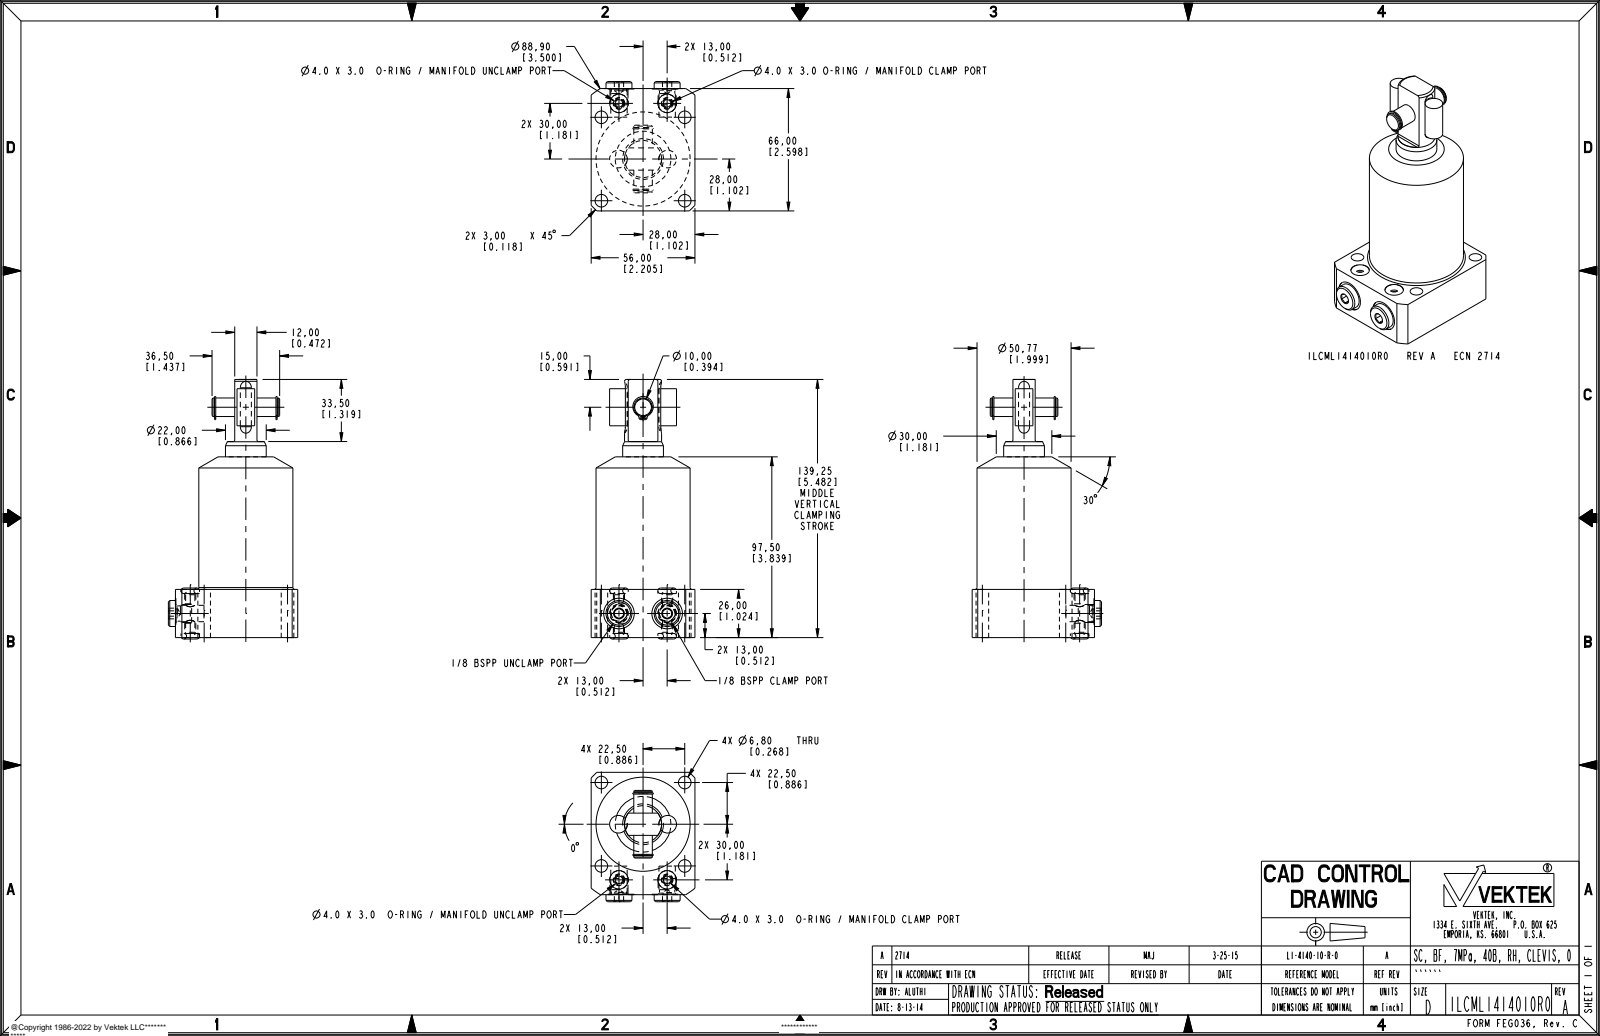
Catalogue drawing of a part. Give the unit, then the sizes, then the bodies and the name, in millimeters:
Units: millimetres
Overall size (bounding box): 140 × 69.81 × 56
Round holes (diameter × count): ⌀6.8 ×4, ⌀1.04 ×2, ⌀5 ×2, ⌀8.84 ×2, ⌀10 ×2, ⌀16.5 ×2
Round bosses / shafts (diameter × count): ⌀14 ×2, ⌀9.73 ×2, ⌀9.53 ×2, ⌀8.25 ×2, ⌀6 ×2, ⌀50.77 ×1, ⌀22 ×1, ⌀20 ×1
Partial cylindrical surfaces — rounded edges, fillets, slot ends (radius × count): R0.8 ×2, R1.04 ×2, R1.48 ×2, R4.76 ×2, R44.45 ×1
Main face-to-face distances: 56, 26, 66, 22, 44, 34, 12, 32, 97.5, 71.5
Hole centre spacings: 45, 12.1, 26, 36.28, 53.35, 63.38, 63.64, 106.25
Volume: 245 885 mm³ · Surface area: 34 940 mm²
Bodies: 7 solids, 234 faces (80 planar, 98 cylindrical, 56 other)
Part name (STEP PRODUCT): ILCML1414010R0
STEP written by: PRO/ENGINEER BY PARAMETRIC TECHNOLOGY CORPORATION, 2013320 (AUTOMOTIVE_DESIGN)
